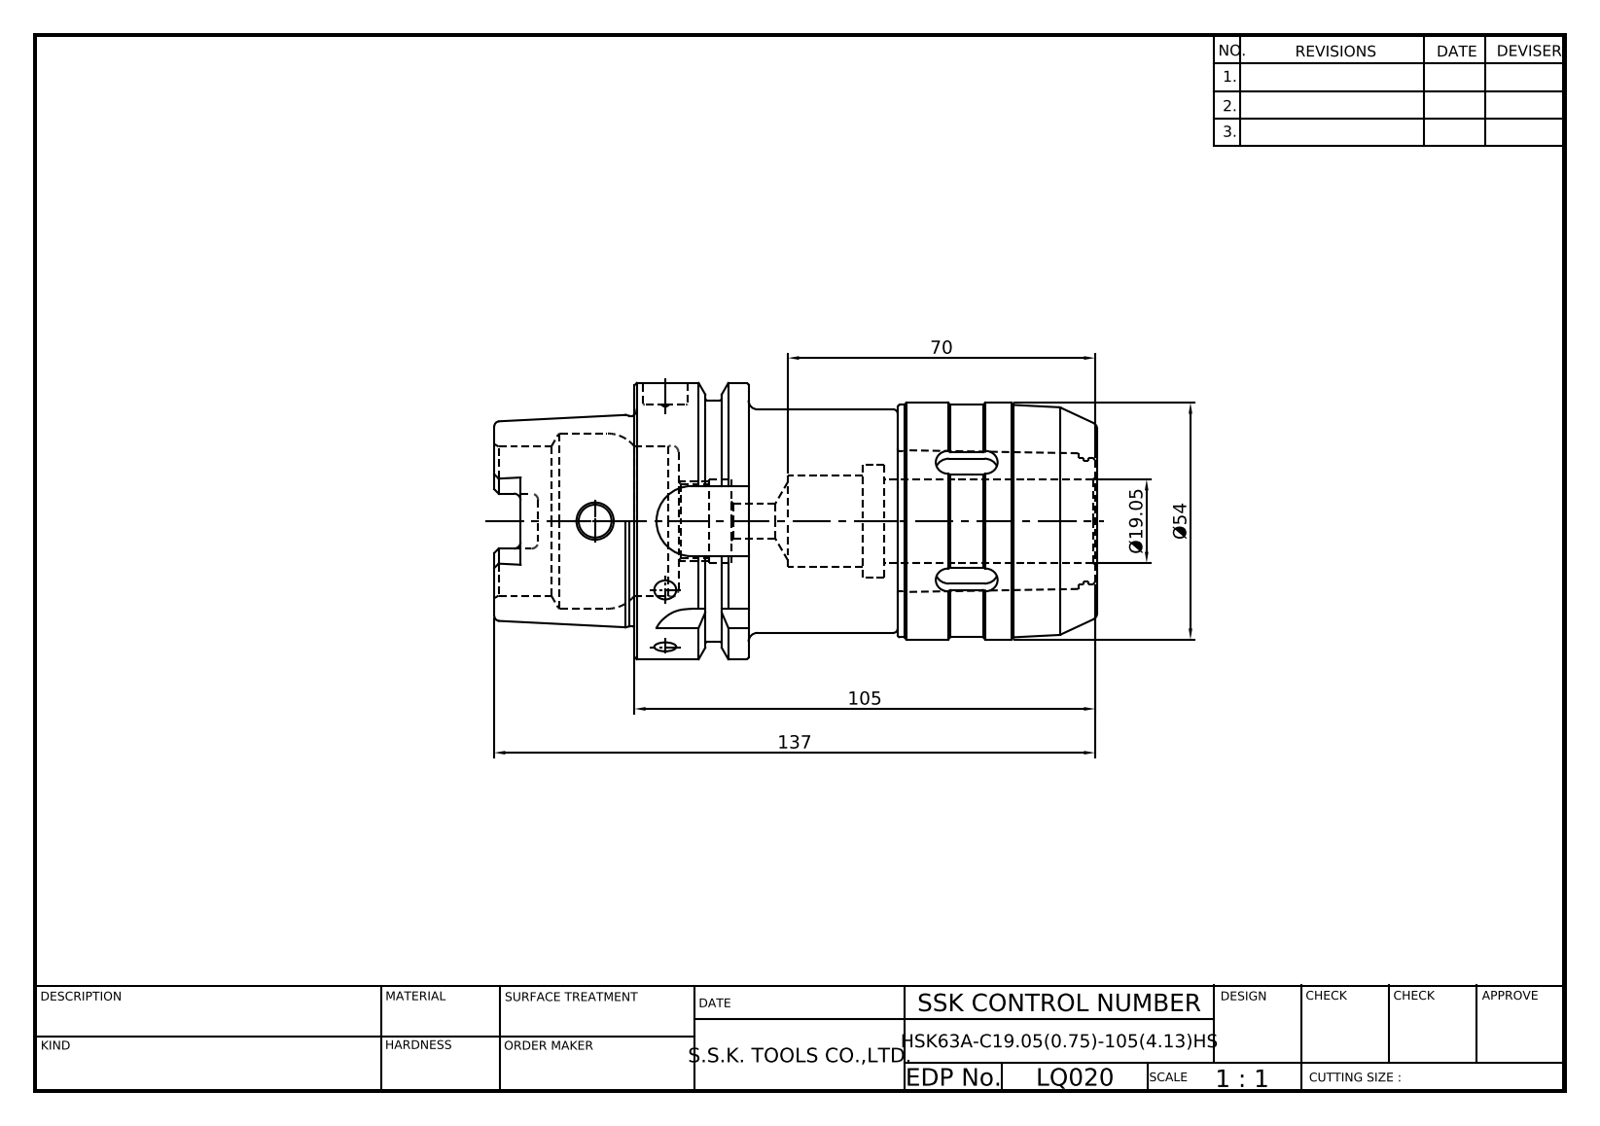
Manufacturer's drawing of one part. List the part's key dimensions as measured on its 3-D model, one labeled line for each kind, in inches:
Part name (STEP PRODUCT): HSK63A-C19.05-105HS; LO-HSK63A-C19.05-105HS; C20-CAP
STEP written by: Autodesk Inventor 2024 (AUTOMOTIVE_DESIGN)
Units: inches
Bodies: 2 solids, 204 faces (70 planar, 61 cylindrical, 73 other)
Overall size (bounding box): 5.413 × 2.48 × 2.48
Volume: 13.02 in³ · Surface area: 81.77 in²
Round holes (diameter × count): ⌀0.295 ×1, ⌀0.315 ×1, ⌀0.394 ×1, ⌀0.666 ×1, ⌀0.748 ×1, ⌀0.75 ×1, ⌀0.827 ×1, ⌀1.008 ×1, ⌀1.339 ×1, ⌀1.539 ×1, ⌀1.575 ×1, ⌀1.614 ×1
Round bosses / shafts (diameter × count): ⌀2.48 ×1, ⌀2.165 ×1, ⌀2.126 ×1, ⌀2.087 ×1, ⌀2.008 ×1, ⌀1.891 ×1, ⌀1.138 ×1
Partial cylindrical surfaces — rounded edges, fillets, slot ends (radius × count): R0.059 ×6, R0.118 ×6, R0.113 ×4, R0.315 ×4
Main face-to-face distances: 1.024, 2.362, 1.339, 0.394, 0.984, 0.63, 1.969, 1.654, 0.866, 1.378
